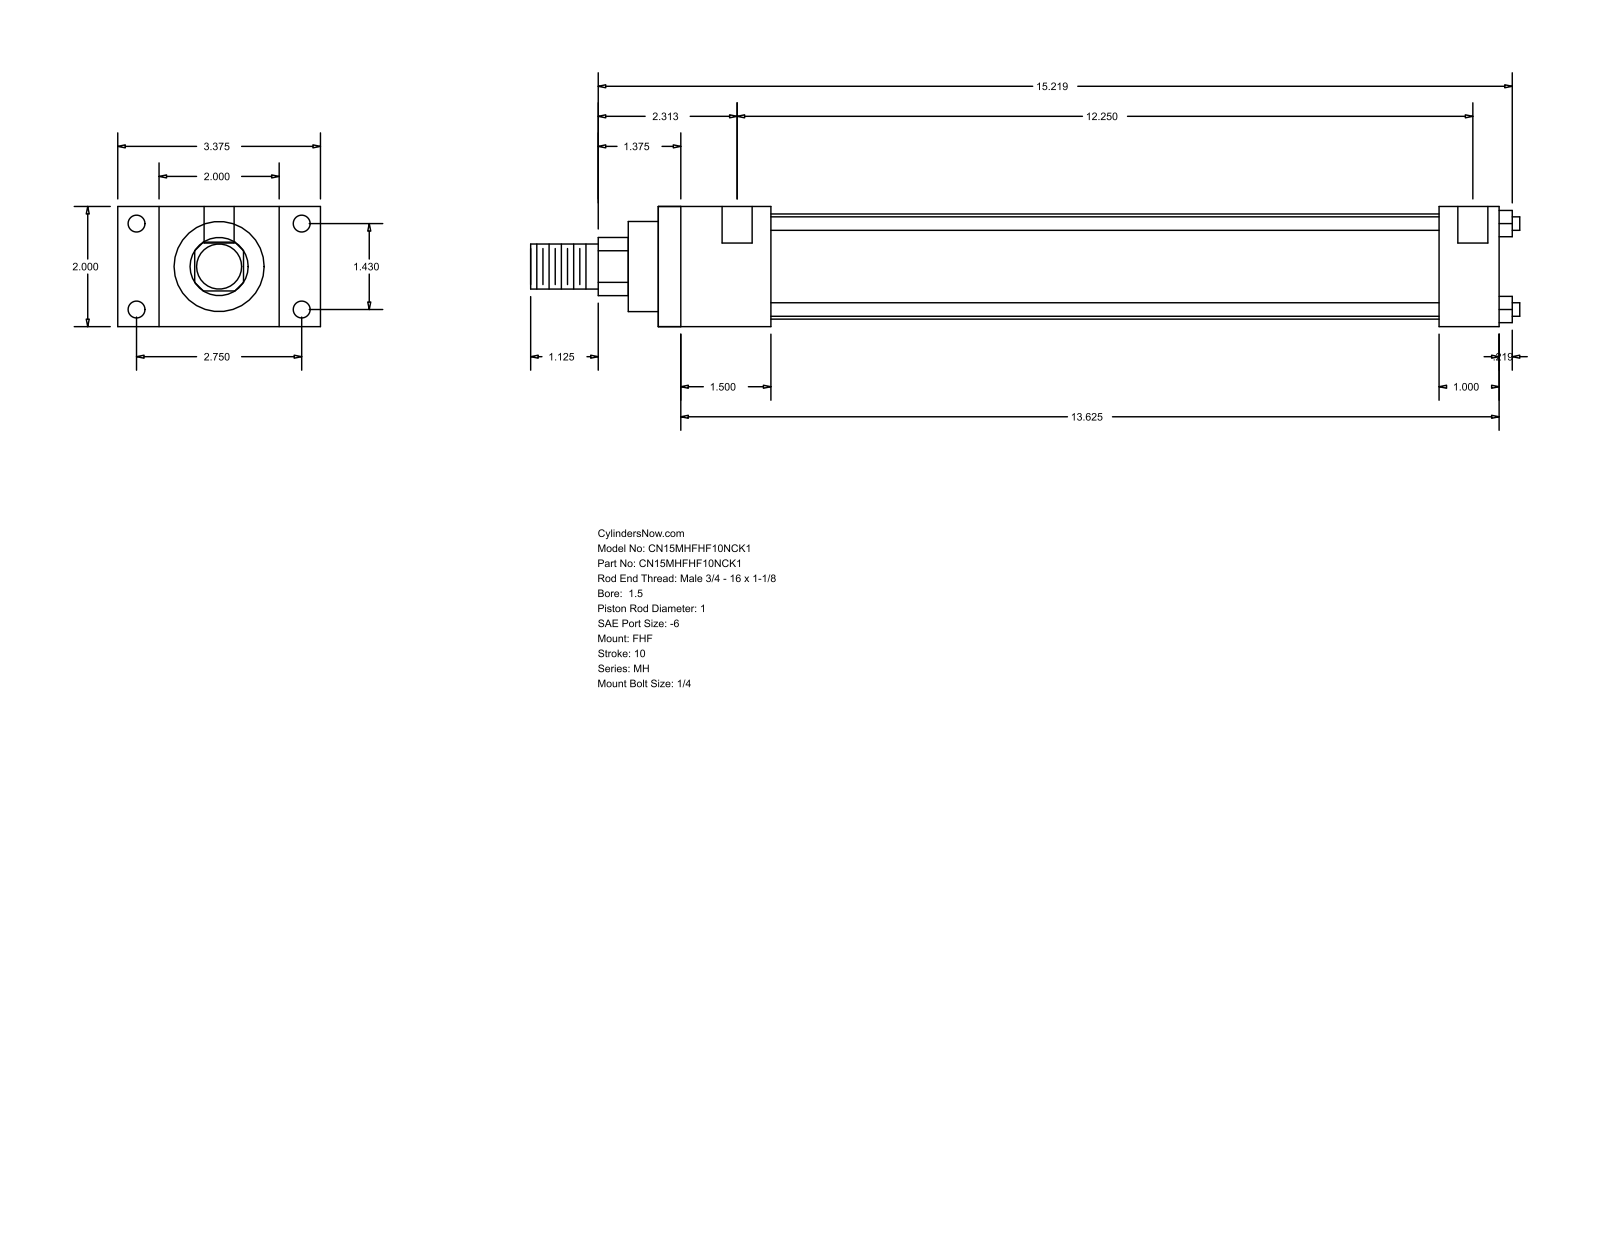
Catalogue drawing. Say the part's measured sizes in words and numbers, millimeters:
The part is named "MH_FHF__0150_1". Its 3-D file was written by "GSSL Pune (CONFIG_CONTROL_DESIGN)". It is 0 solids with 88 faces: 60 planar, 28 cylindrical and 0 other. Overall it measures 418.31 by 85.72 by 50.8 millimeters. Round holes: 4 of diameter 5.56, 4 of diameter 7.14, 2 of diameter 12.7. Round bosses or shafts: 4 of diameter 5.71, 1 of diameter 44.45, 1 of diameter 38.1, 1 of diameter 25.4, 1 of diameter 19.05. Partial cylindrical surfaces (rounded edges, fillets, slot ends): 1 of radius 12.29. The main face-to-face distances are 50.8, 17.46, 68.26, 47.63, 85.72, 355.6, 307.97, 25.4, 330.2, 282.57. The hole center spacings are 36.32, 69.84, 78.72, 314.33, 3.18, 311.15.
